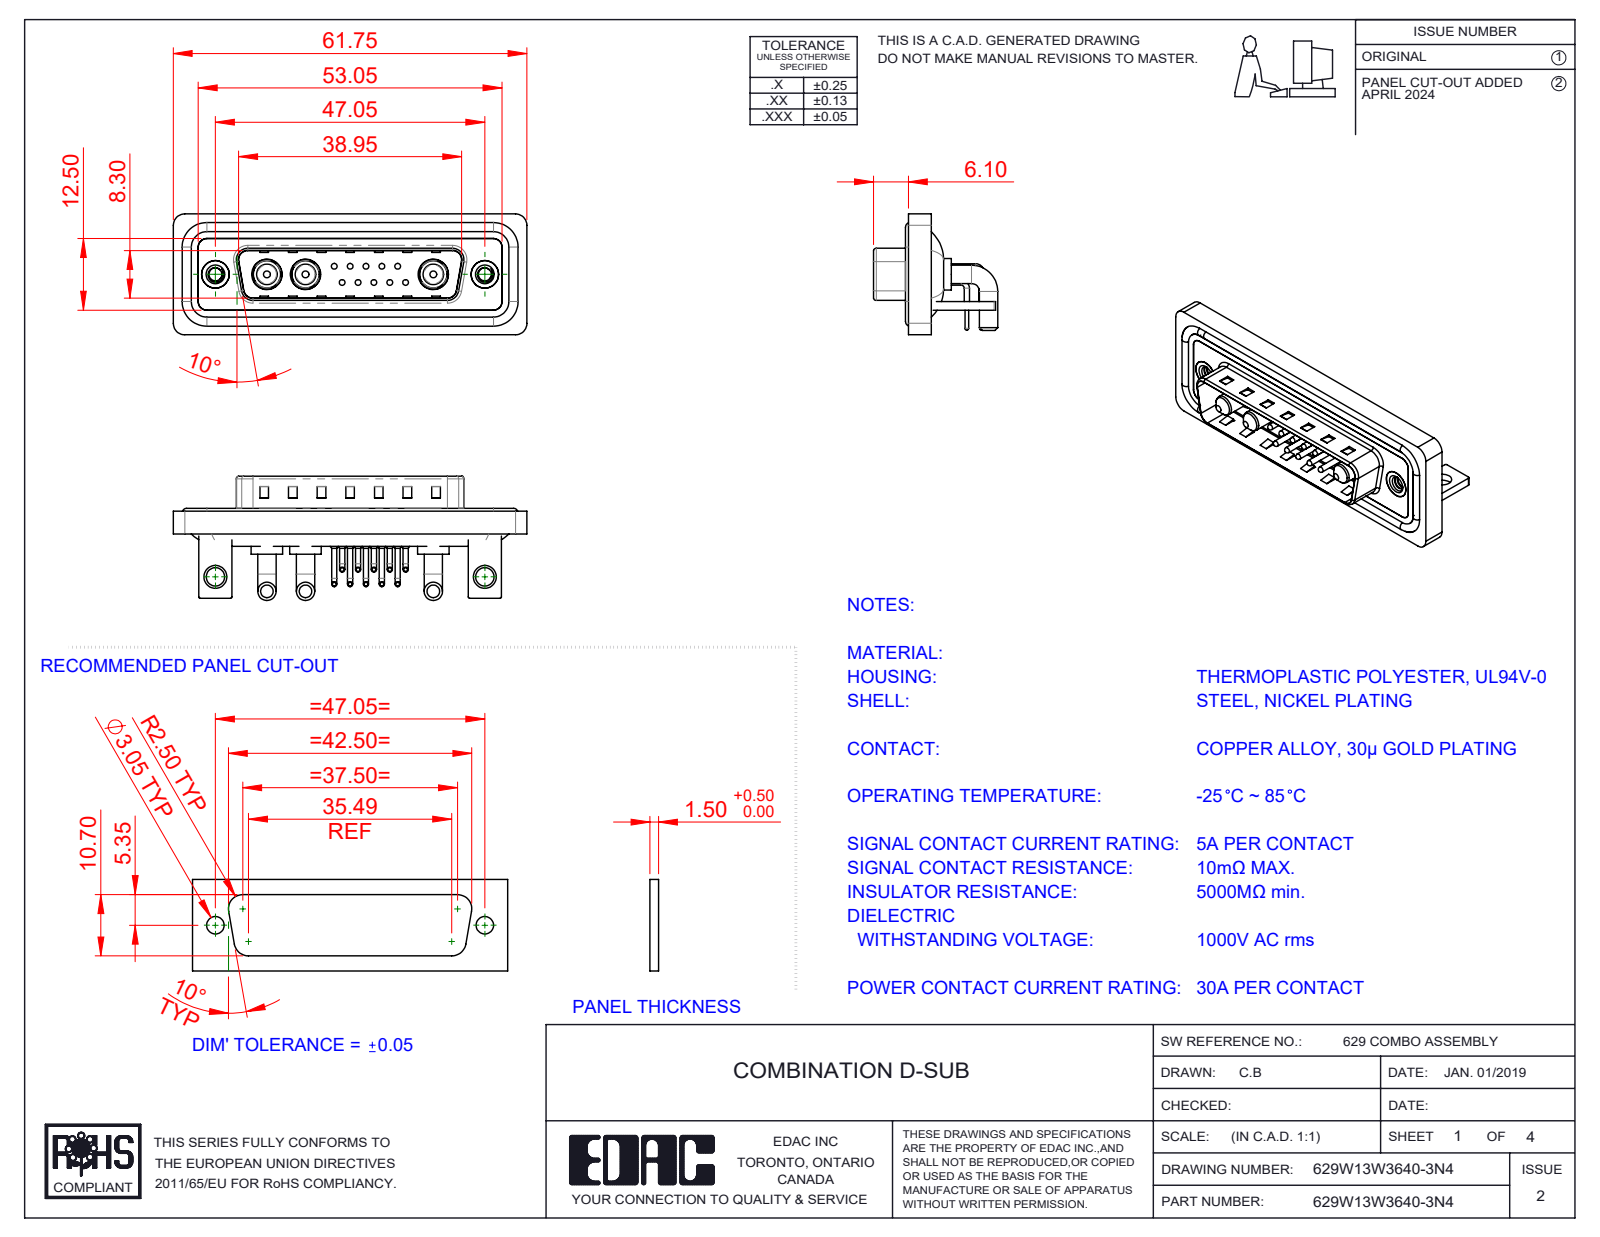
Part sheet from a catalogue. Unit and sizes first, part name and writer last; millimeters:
Units: millimetres
Overall size (bounding box): 61.75 × 21.7 × 21.1
Round holes (diameter × count): ⌀0.75 ×10, ⌀1.6 ×10, ⌀2 ×10, ⌀4.85 ×3, ⌀5.3 ×3, ⌀2.26 ×2, ⌀3.2 ×2, ⌀4 ×2, ⌀4.8 ×2, ⌀5 ×2
Round bosses / shafts (diameter × count): ⌀0.9 ×20, ⌀1.5 ×10, ⌀1 ×10, ⌀0.65 ×10, ⌀3.2 ×6, ⌀1.6 ×4, ⌀5.5 ×3, ⌀5.2 ×3
Partial cylindrical surfaces — rounded edges, fillets, slot ends (radius × count): R2 ×19, R1.5 ×18, R0.25 ×16, R1.01 ×10, R0.5 ×9, R1.6 ×8, R0.6 ×4, R0.65 ×4
Main face-to-face distances: 0.4, 0.8, 1.5, 2.9, 2.1, 1.1, 4.1, 1.6, 3.7, 4.5
Hole centre spacings: 3.16, 2.77, 5.04, 5.54, 7.49, 5.03, 8.31, 10.11
Volume: 7 972 mm³ · Surface area: 13 138 mm²
Bodies: 25 solids, 1752 faces (899 planar, 629 cylindrical, 224 other)
Part name (STEP PRODUCT): 629Combo Shell Front_25 Contacts; 629Combo Contact Row 2; 629Combo Waterproof Housing_25 Contacts; 629Combo Housing_13W3 (+6 more)
STEP written by: SolidWorks 2023 (CONFIG_CONTROL_DESIGN)
